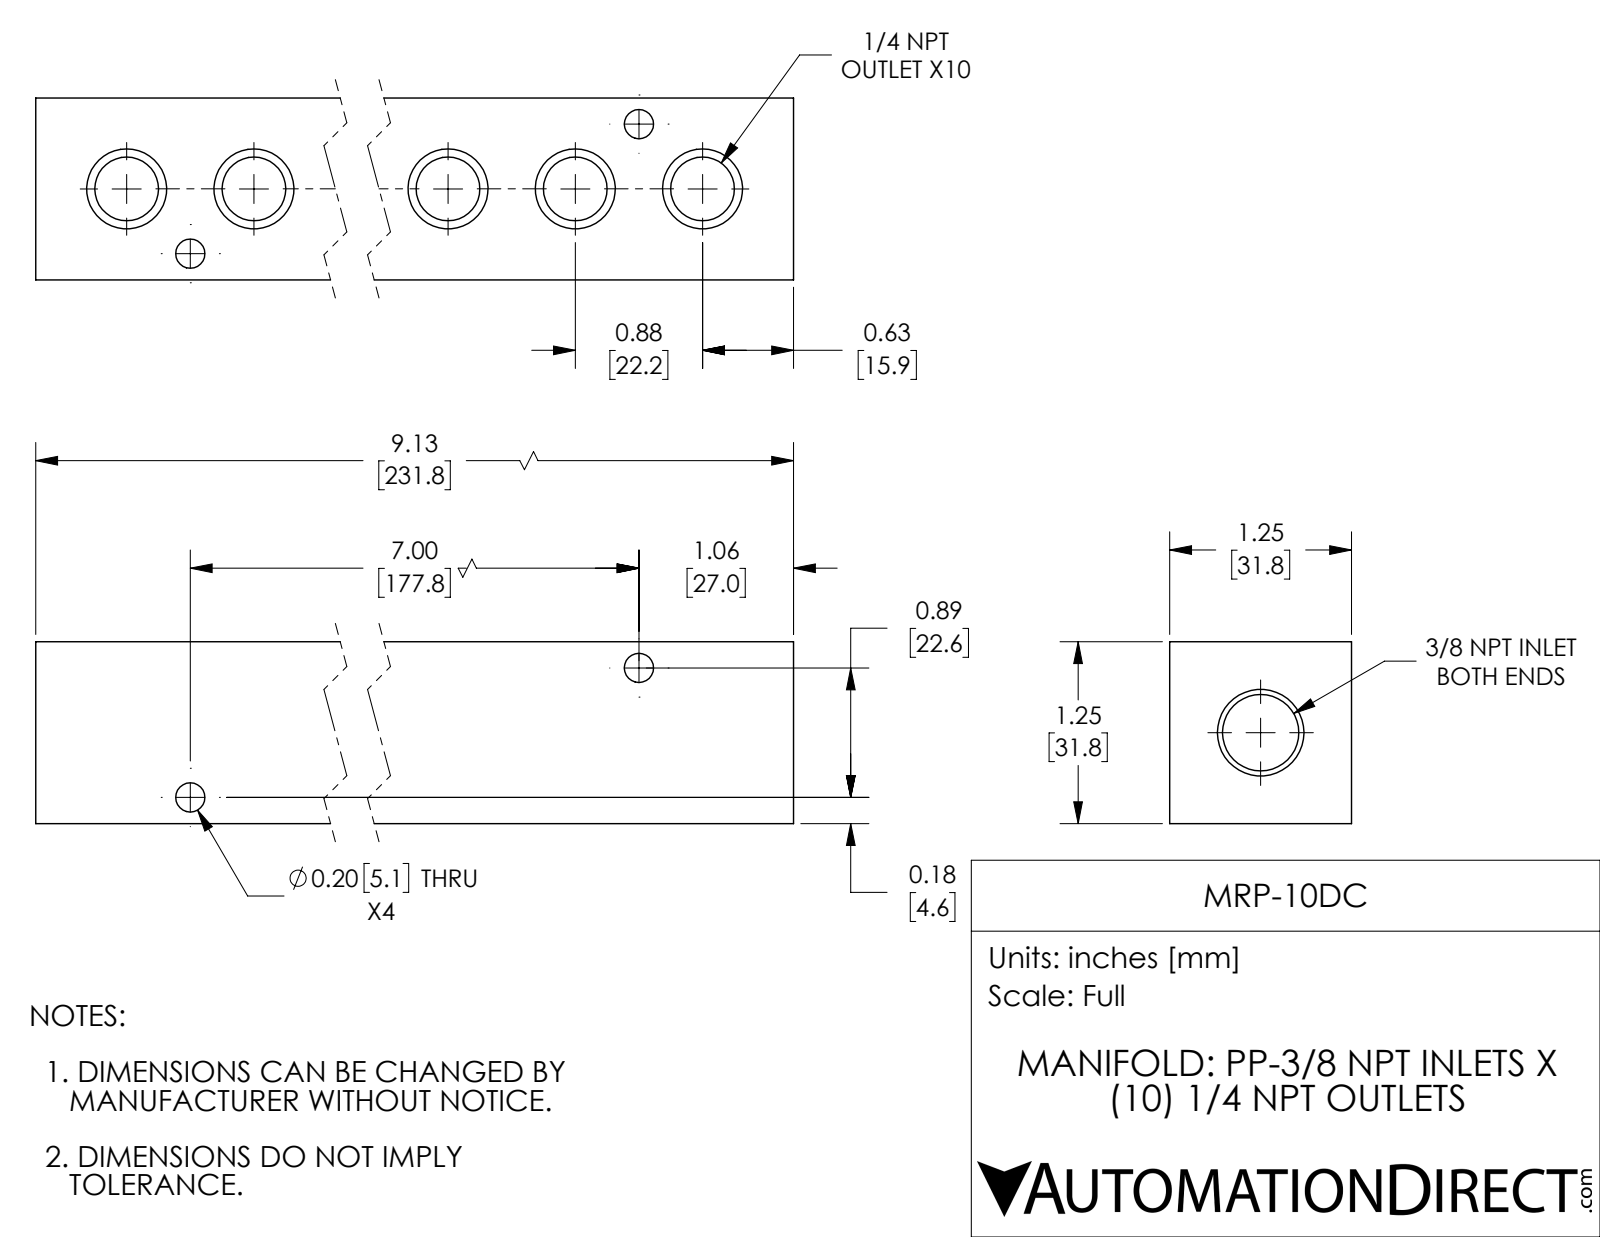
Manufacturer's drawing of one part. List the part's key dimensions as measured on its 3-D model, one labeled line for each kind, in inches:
Part name (STEP PRODUCT): MRP-10DC
STEP written by: SolidWorks 2018 (AUTOMOTIVE_DESIGN)
Units: inches
Bodies: 1 solid, 68 faces (6 planar, 38 cylindrical, 24 other)
Overall size (bounding box): 9.125 × 1.25 × 1.25
Volume: 11.52 in³ · Surface area: 68.01 in²
Round holes (diameter × count): ⌀0.438 ×10, ⌀0.201 ×4, ⌀0.525 ×1
Main face-to-face distances: 1.25, 9.125
Hole centre spacings: 1.75, 0.875, 3.5, 0.624, 0.875, 2.625, 2.625, 4.375
